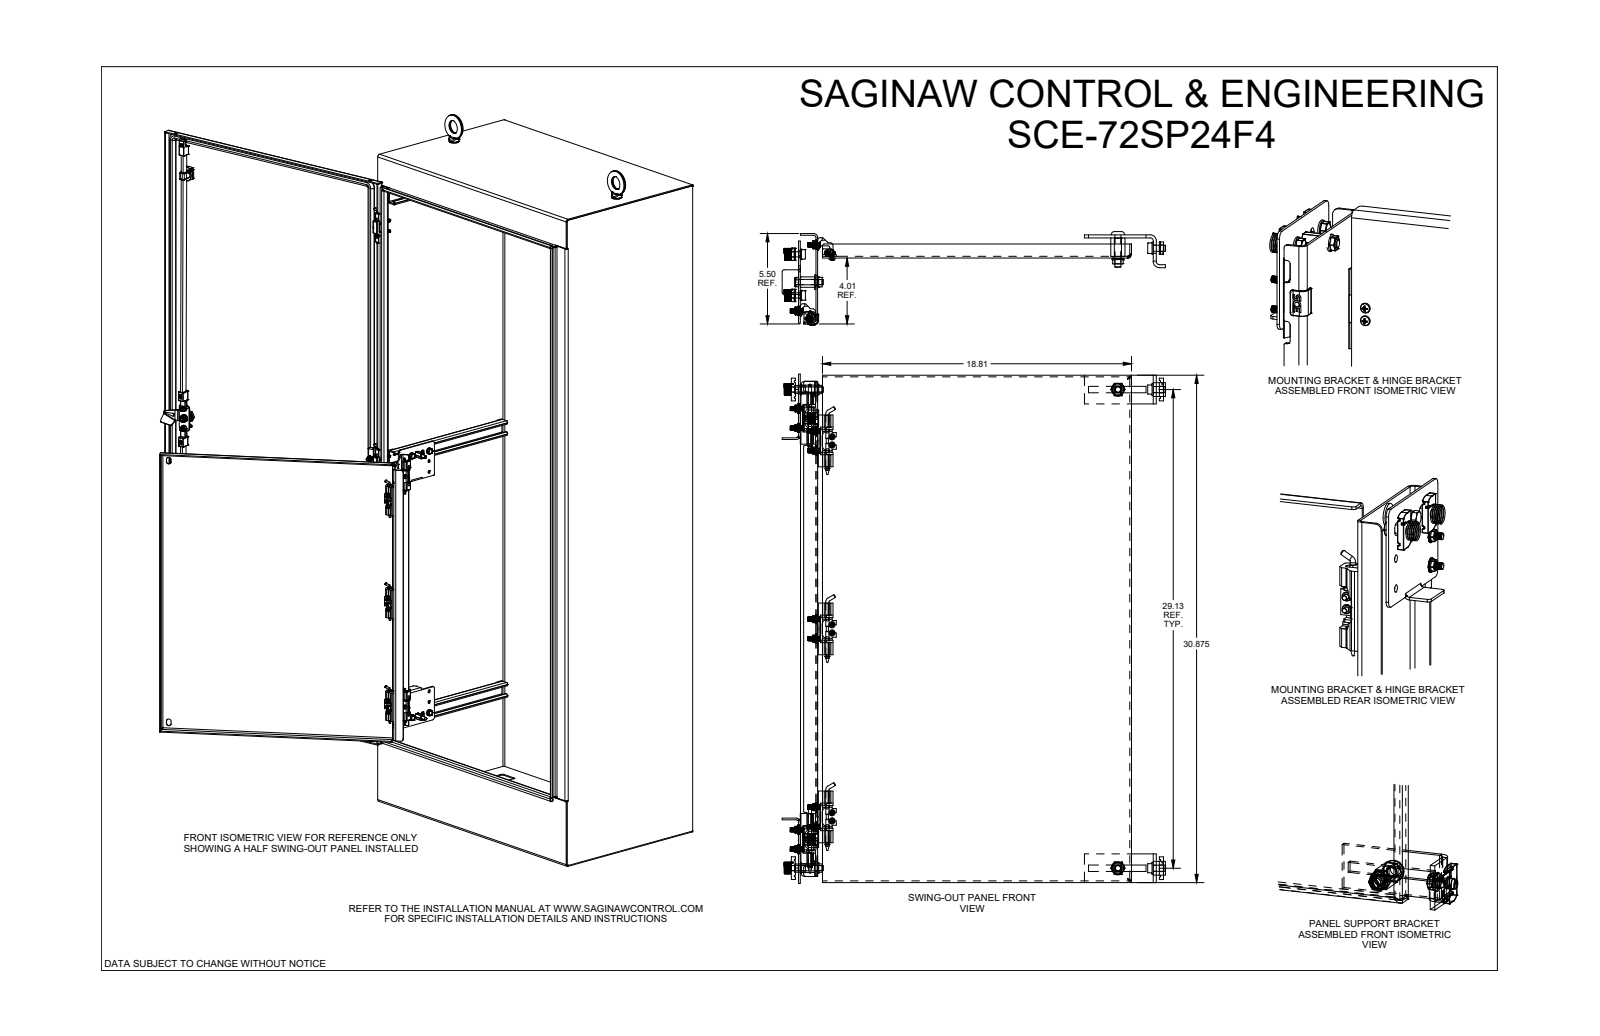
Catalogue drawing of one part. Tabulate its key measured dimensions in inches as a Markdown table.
| quantity | value |
| --- | --- |
| part name | SCE-72SP24F4 |
| STEP written by | SolidWorks 2021 (AUTOMOTIVE_DESIGN) |
| units | inches |
| bodies | 39 solids, 1855 faces (892 planar, 705 cylindrical, 258 other) |
| overall size | 30.994 × 23.336 × 5.671 |
| volume | 104.1 in³ |
| surface area | 1 969 in² |
| round holes (diameter × count) | 0.25 × 16, 0.281 × 14, 0.36 × 10, 0.218 × 8, 0.19 × 6, 0.04 × 5, 0.201 × 3, 0.156 × 2, 0.33 × 2, 0.375 × 2, 0.383 × 2, 0.204 × 1 |
| round bosses / shafts (diameter × count) | 0.196 × 7, 0.34 × 6, 0.249 × 6, 0.886 × 2, 0.813 × 2, 0.5 × 2, 0.368 × 2, 0.31 × 2 |
| partial cylindrical surfaces (radius × count) | 0.011 × 36, 0.015 × 20, 0.188 × 16, 0.25 × 16, 0.1 × 14, 0.06 × 11, 0.07 × 11, 0.025 × 10 |
| main face-to-face distances | 0.104, 1.058, 1.385, 19.108, 20.166, 0.954, 1.162, 5.396, 4.011, 30.771 |
| hole center spacings | 0.592, 11.437, 25.625, 1.181, 22.875, 2.098, 2.92, 3.5 |
